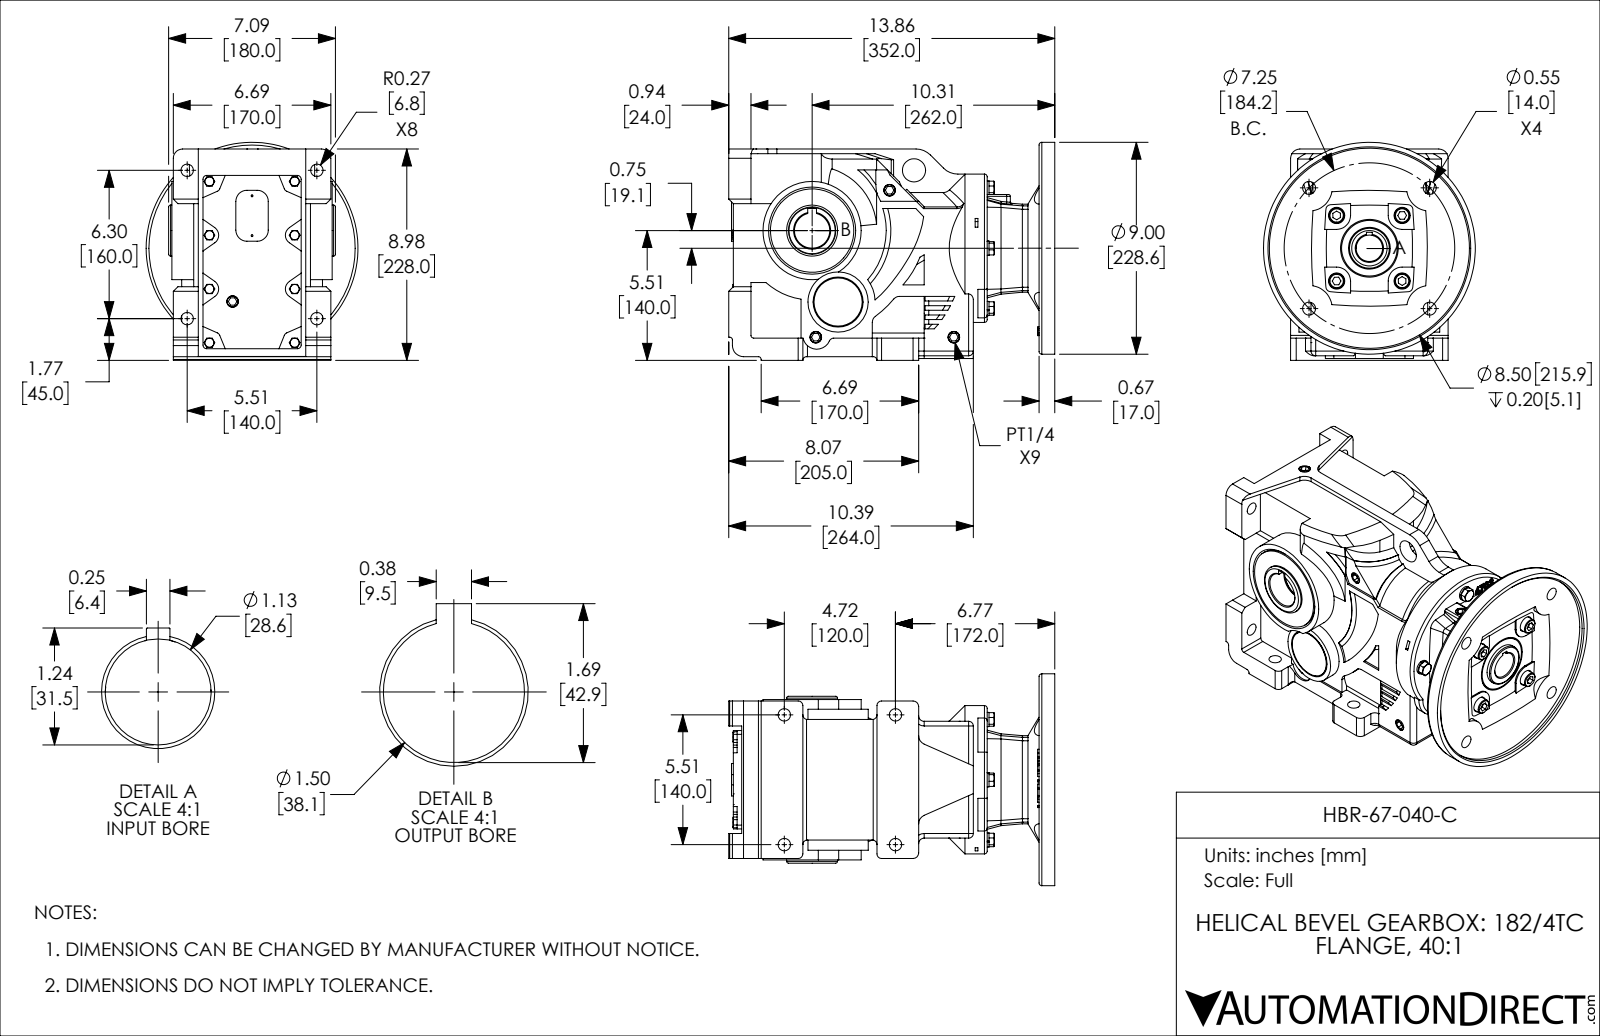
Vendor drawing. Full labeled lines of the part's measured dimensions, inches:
Part name (STEP PRODUCT): HBR-67-040-C
STEP written by: SolidWorks 2018 (AUTOMOTIVE_DESIGN)
Units: inches
Bodies: 1 solid, 1100 faces (560 planar, 258 cylindrical, 282 other)
Overall size (bounding box): 13.858 × 9.262 × 9
Volume: 513.2 in³ · Surface area: 714.3 in²
Round holes (diameter × count): ⌀0.531 ×8, ⌀0.323 ×4, ⌀0.354 ×4, ⌀0.551 ×4, ⌀0.689 ×4, ⌀0.079 ×2, ⌀0.984 ×1, ⌀1.125 ×1, ⌀1.417 ×1, ⌀1.5 ×1, ⌀1.575 ×1, ⌀8.5 ×1
Round bosses / shafts (diameter × count): ⌀0.63 ×4, ⌀0.606 ×4, ⌀0.315 ×4, ⌀9 ×1, ⌀6.299 ×1, ⌀4.173 ×1, ⌀3.543 ×1, ⌀2.559 ×1
Partial cylindrical surfaces — rounded edges, fillets, slot ends (radius × count): R0.197 ×20, R0.157 ×12, R0.394 ×11, R0.079 ×7, R0.472 ×5, R0.591 ×5, R0.236 ×4, R0.689 ×4
Main face-to-face distances: 0.197, 0.079, 0.469, 0.945, 0.059, 13.461, 12.992, 8.78, 4.961, 0.118
Hole centre spacings: 2.563, 5.728, 1.656, 1.817, 2.559, 3.619, 4.125, 4.125
